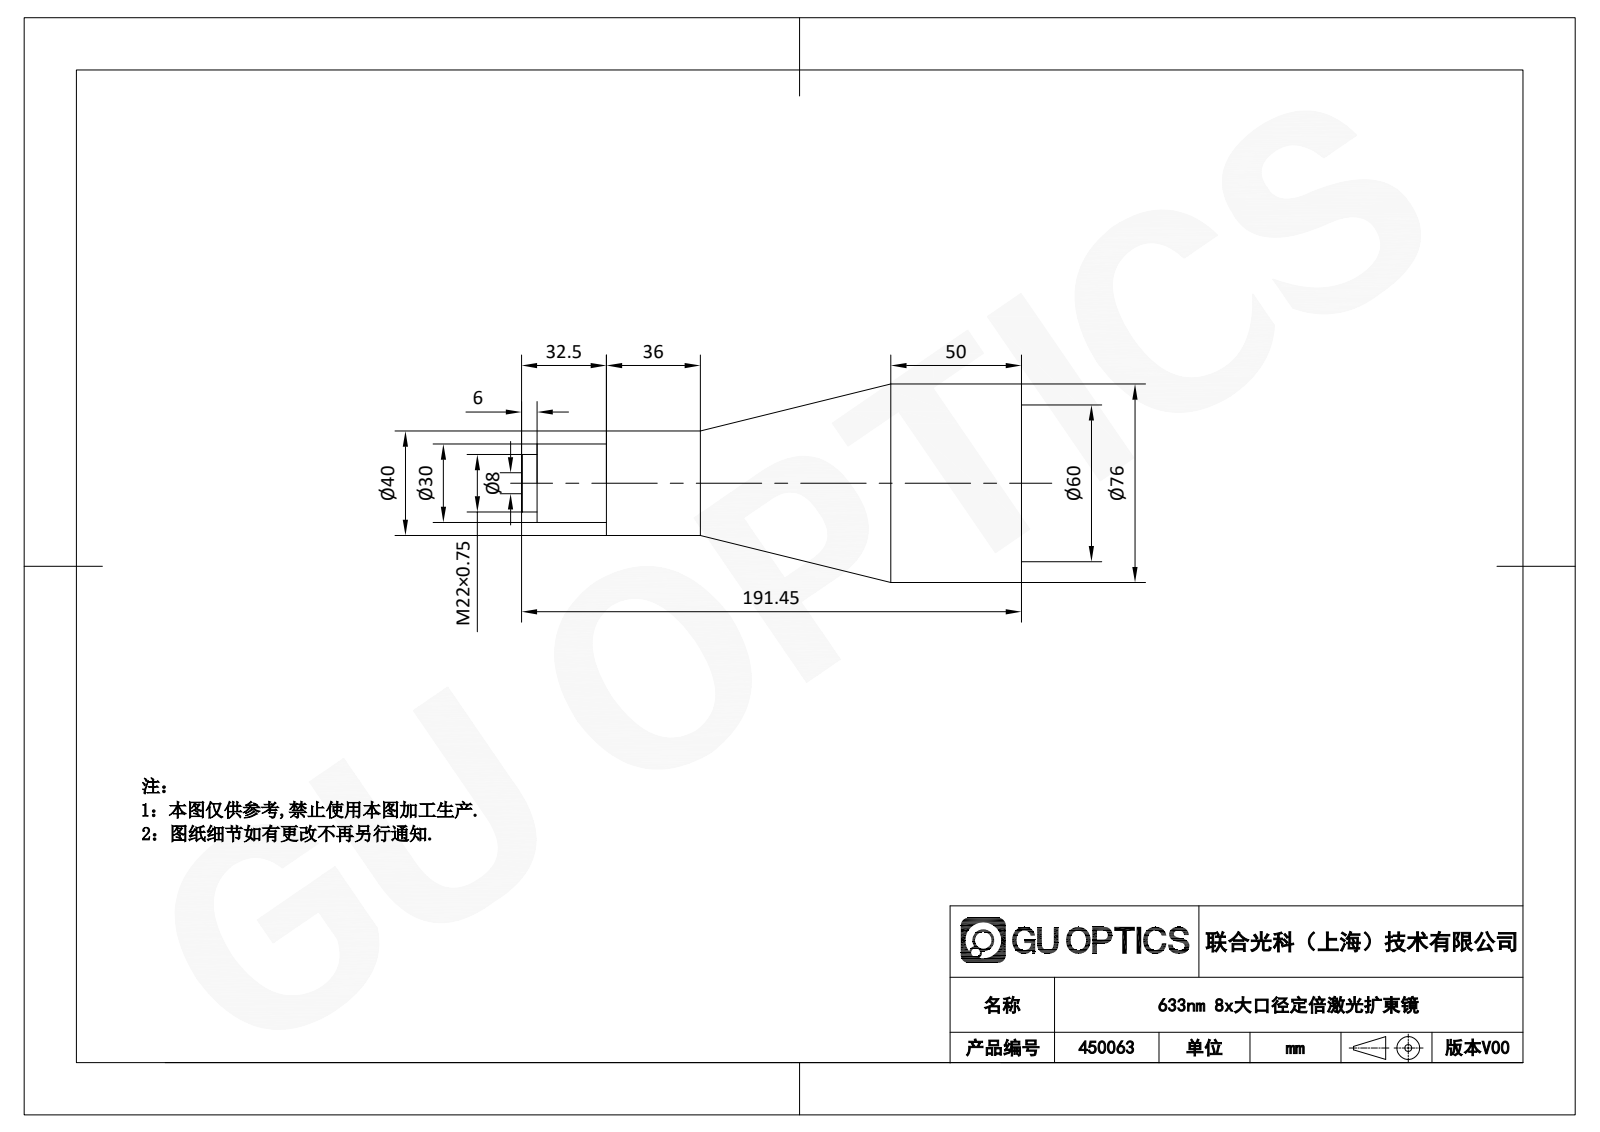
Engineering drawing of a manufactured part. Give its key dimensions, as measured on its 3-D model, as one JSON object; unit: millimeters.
{"part_name": "450063", "step_written_by": "SolidWorks 2020 (AUTOMOTIVE_DESIGN)", "units": "millimeters", "bodies": {"solids": 1, "faces": 22, "planar": 6, "cylindrical": 12, "other": 4}, "overall_size": [191.45, 76, 76], "volume_mm3": 489122, "surface_area_mm2": 39062, "round_holes": [[8, 1], [60, 1]], "round_bosses_or_shafts": [[76, 1], [40, 1], [30, 1], [22, 1]], "face_to_face_distances": [1, 157.95, 158.95, 190.45, 26.5, 184.45, 185.45, 6, 32.5, 191.45]}
